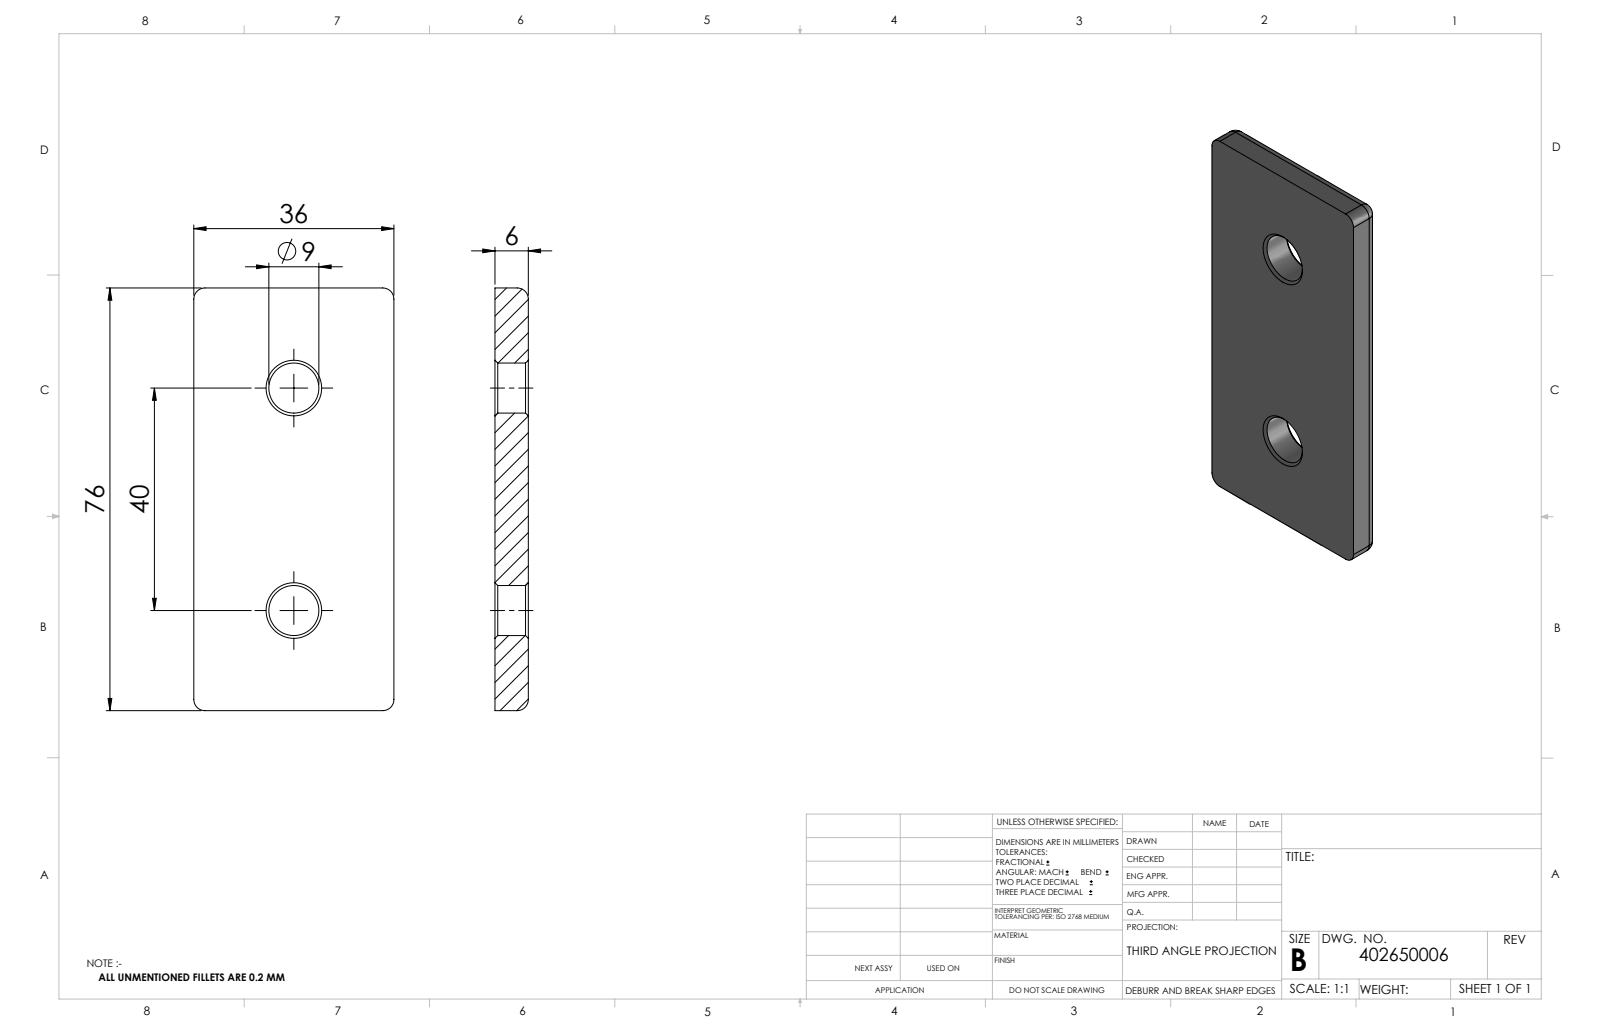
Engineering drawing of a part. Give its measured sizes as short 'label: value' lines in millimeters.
name: 402650006
written by: SolidWorks 2014 (CONFIG_CONTROL_DESIGN)
unit: mm
bodies: 1 solid, 30 faces (6 planar, 12 cylindrical, 12 other)
size: 76 × 36 × 6
volume: 15 430 mm³; area: 6 650 mm²
holes: 2× ⌀9
rounds: 8× R2
face distances: 6, 36, 76
hole spacings: 40
